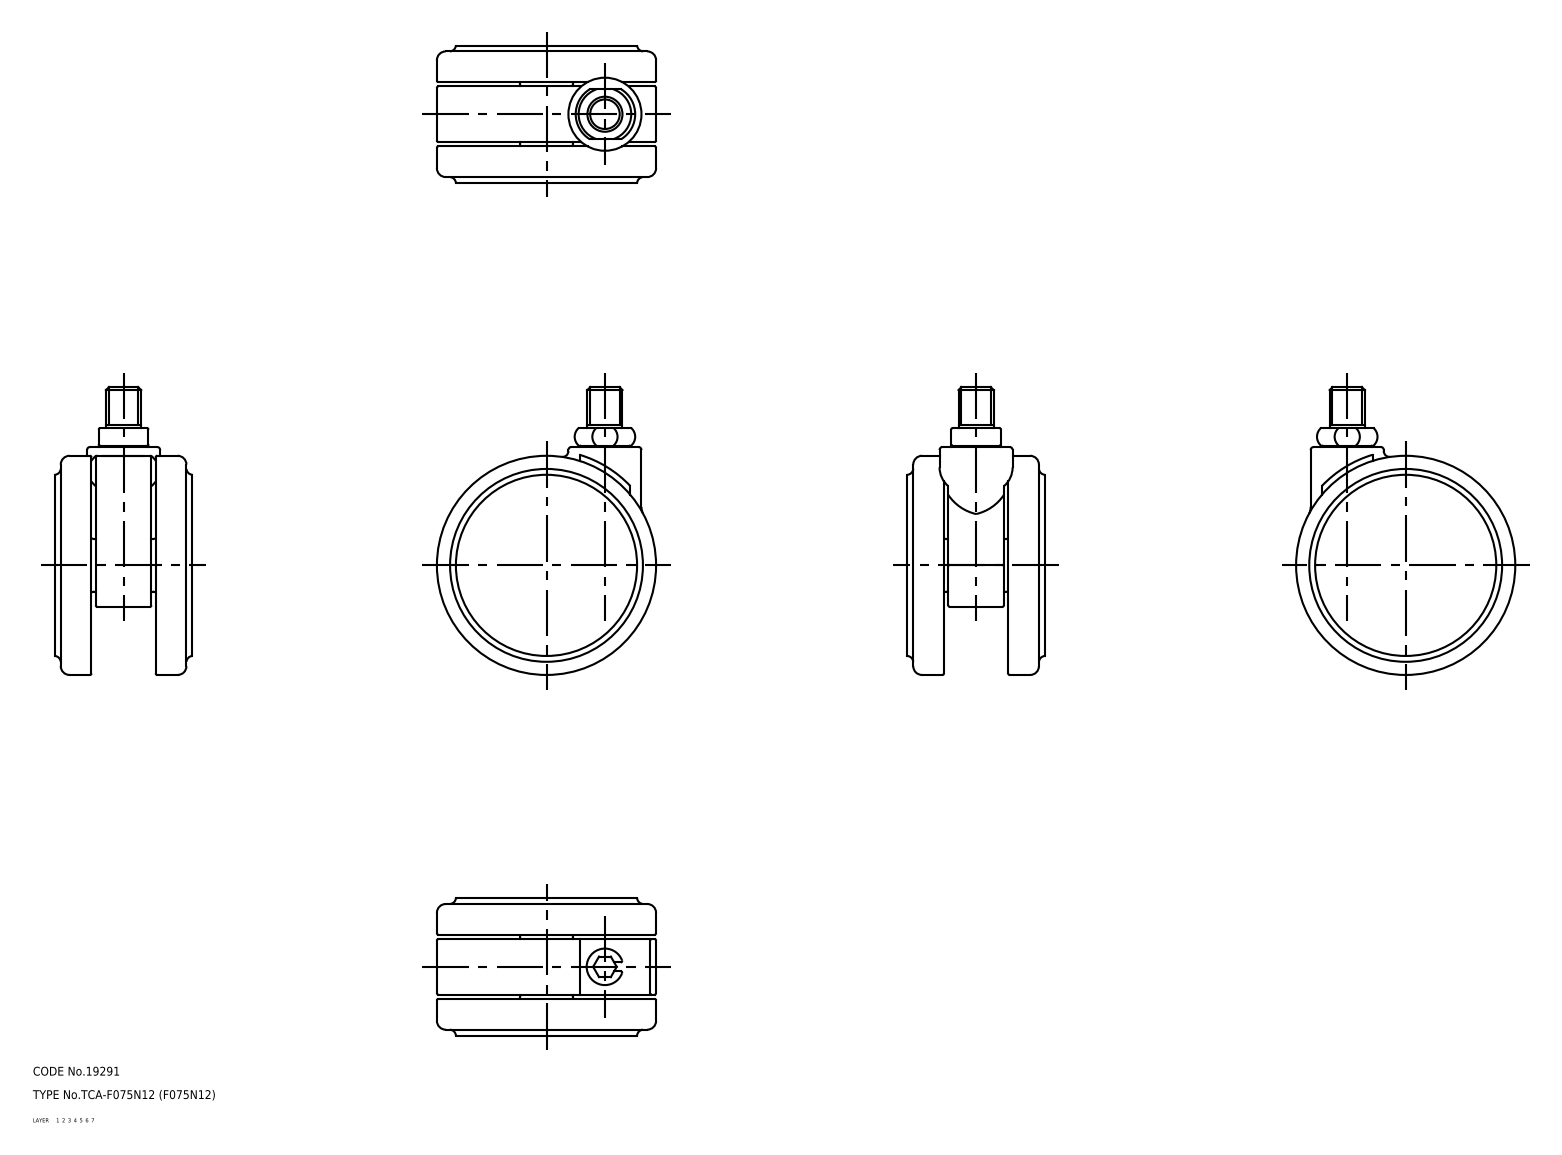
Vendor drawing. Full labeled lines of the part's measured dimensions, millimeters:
Part name (STEP PRODUCT): 67116585; 67116598; 67116611; 67116624
STEP written by: CADfix (AUTOMOTIVE_DESIGN)
Units: millimetres
Bodies: 4 solids, 122 faces (0 planar, 0 cylindrical, 122 other)
Overall size (bounding box): 98.5 × 75 × 47
Volume: 160 541 mm³ · Surface area: 36 982 mm²
